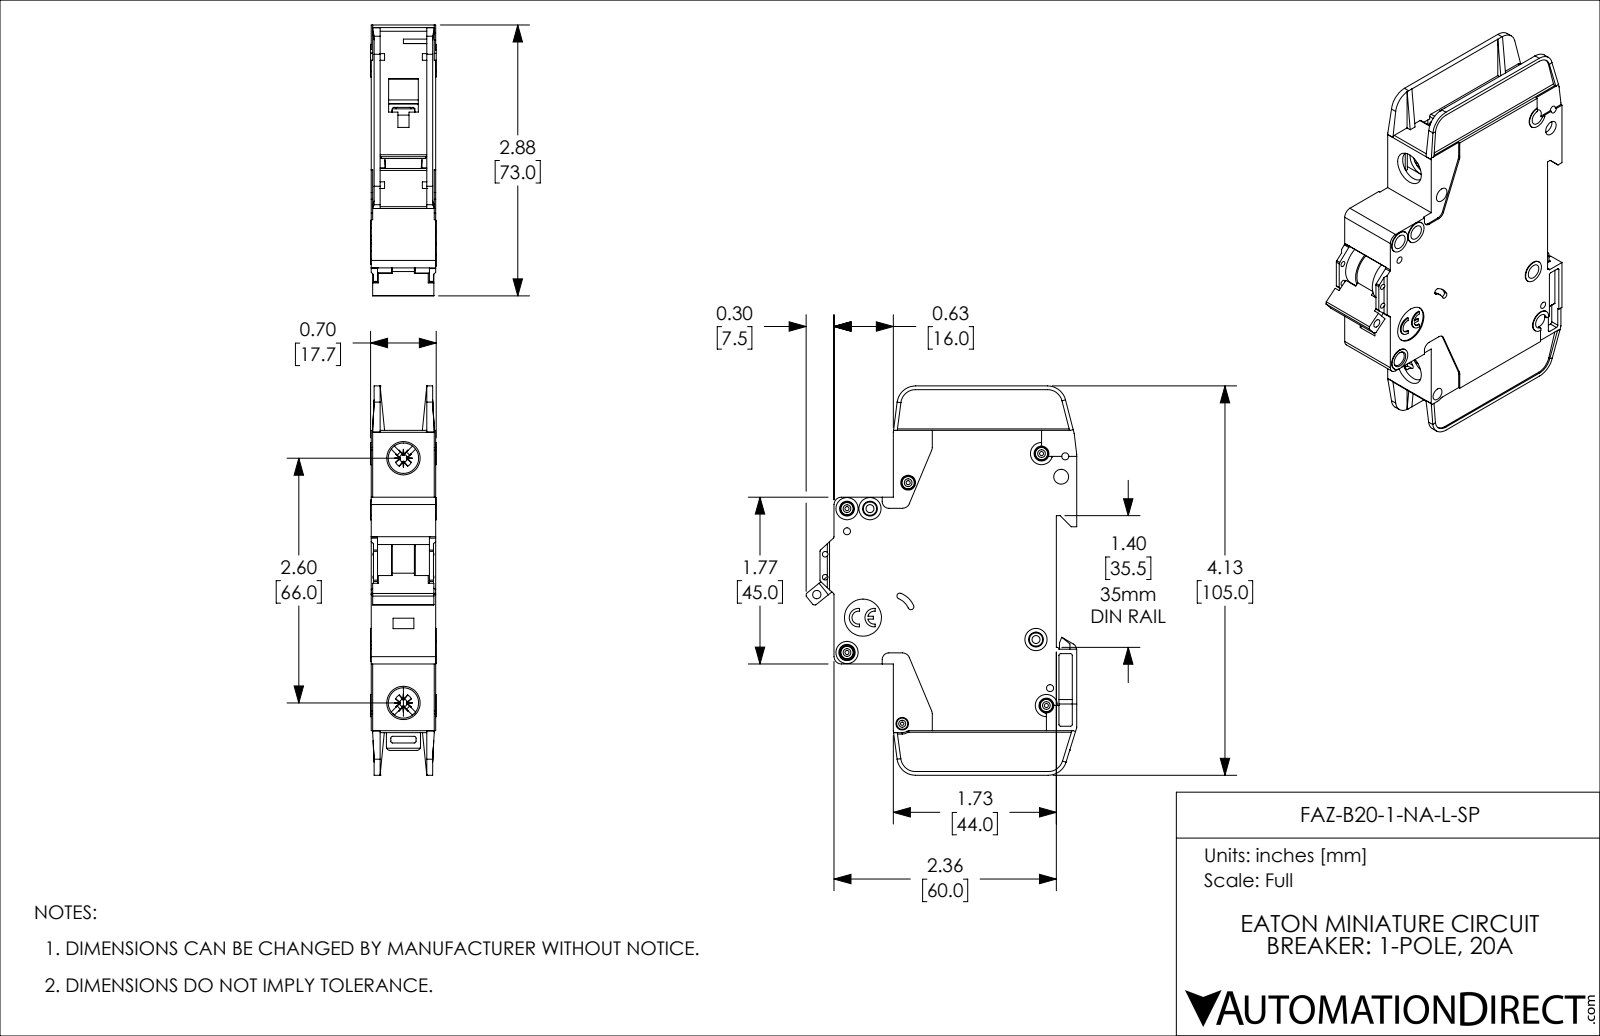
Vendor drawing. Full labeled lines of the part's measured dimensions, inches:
Part name (STEP PRODUCT): FAZ-B20-1-NA-L-SP
STEP written by: SolidWorks 2019 (AUTOMOTIVE_DESIGN)
Units: inches
Bodies: 1 solid, 1127 faces (671 planar, 357 cylindrical, 99 other)
Overall size (bounding box): 4.134 × 2.876 × 0.697
Volume: 4.682 in³ · Surface area: 41.01 in²
Round holes (diameter × count): ⌀0.157 ×8, ⌀0.043 ×5, ⌀0.075 ×4, ⌀0.059 ×2, ⌀0.085 ×2, ⌀0.323 ×2, ⌀0.035 ×1, ⌀0.089 ×1, ⌀0.098 ×1, ⌀0.134 ×1, ⌀0.394 ×1
Round bosses / shafts (diameter × count): ⌀0.13 ×5, ⌀0.236 ×4, ⌀0.118 ×2, ⌀0.098 ×1
Partial cylindrical surfaces — rounded edges, fillets, slot ends (radius × count): R0.02 ×42, R0.016 ×10, R0.039 ×10, R0.079 ×8, R0.197 ×5, R0.008 ×4, R0.026 ×4, R0.043 ×4
Main face-to-face distances: 0.047, 0.685, 0.591, 0.638, 0.094, 0.543, 0.016, 0.031, 0.496, 0.575
Hole centre spacings: 0.244, 0.537, 0.87, 0.189, 0.199, 0.204, 0.221, 0.24
